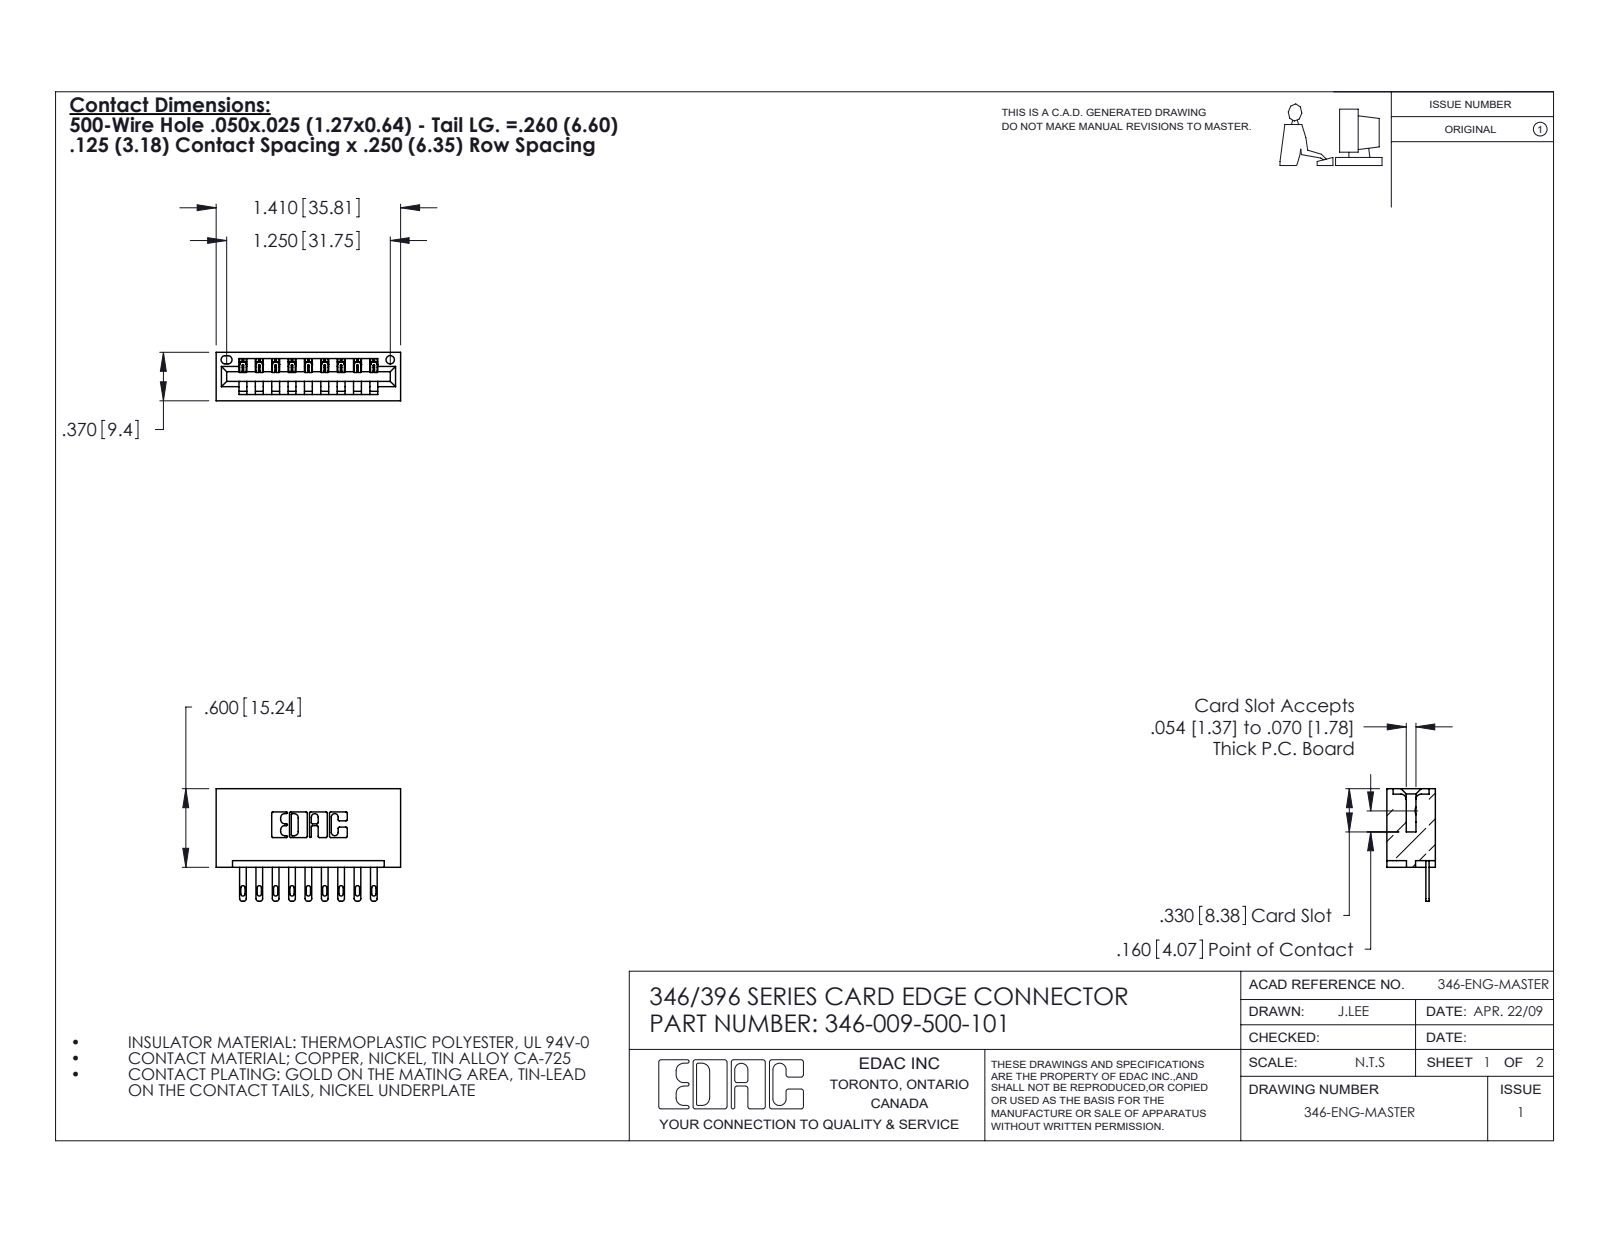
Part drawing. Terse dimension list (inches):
name: 346-009-500-101; 346 Part_No Mounting Lugs; 345-292-001_345-293-100
written by: SolidWorks 2020 (CONFIG_CONTROL_DESIGN)
unit: in
bodies: 10 solids, 600 faces (378 planar, 222 cylindrical, 0 other)
size: 1.41 × 0.86 × 0.37
volume: 0.229 in³; area: 6.873 in²
holes: 1× ⌀0.064
rounds: 22× R0.01, 18× R0.006, 18× R0.016, 18× R0.02, 6× R0.007, 6× R0.031, 3× R0.026, 2× R0.031
face distances: 0.25, 0.048, 0.322, 0.37, 0.5, 0.072, 0.298, 0.025, 0.125, 0.185
